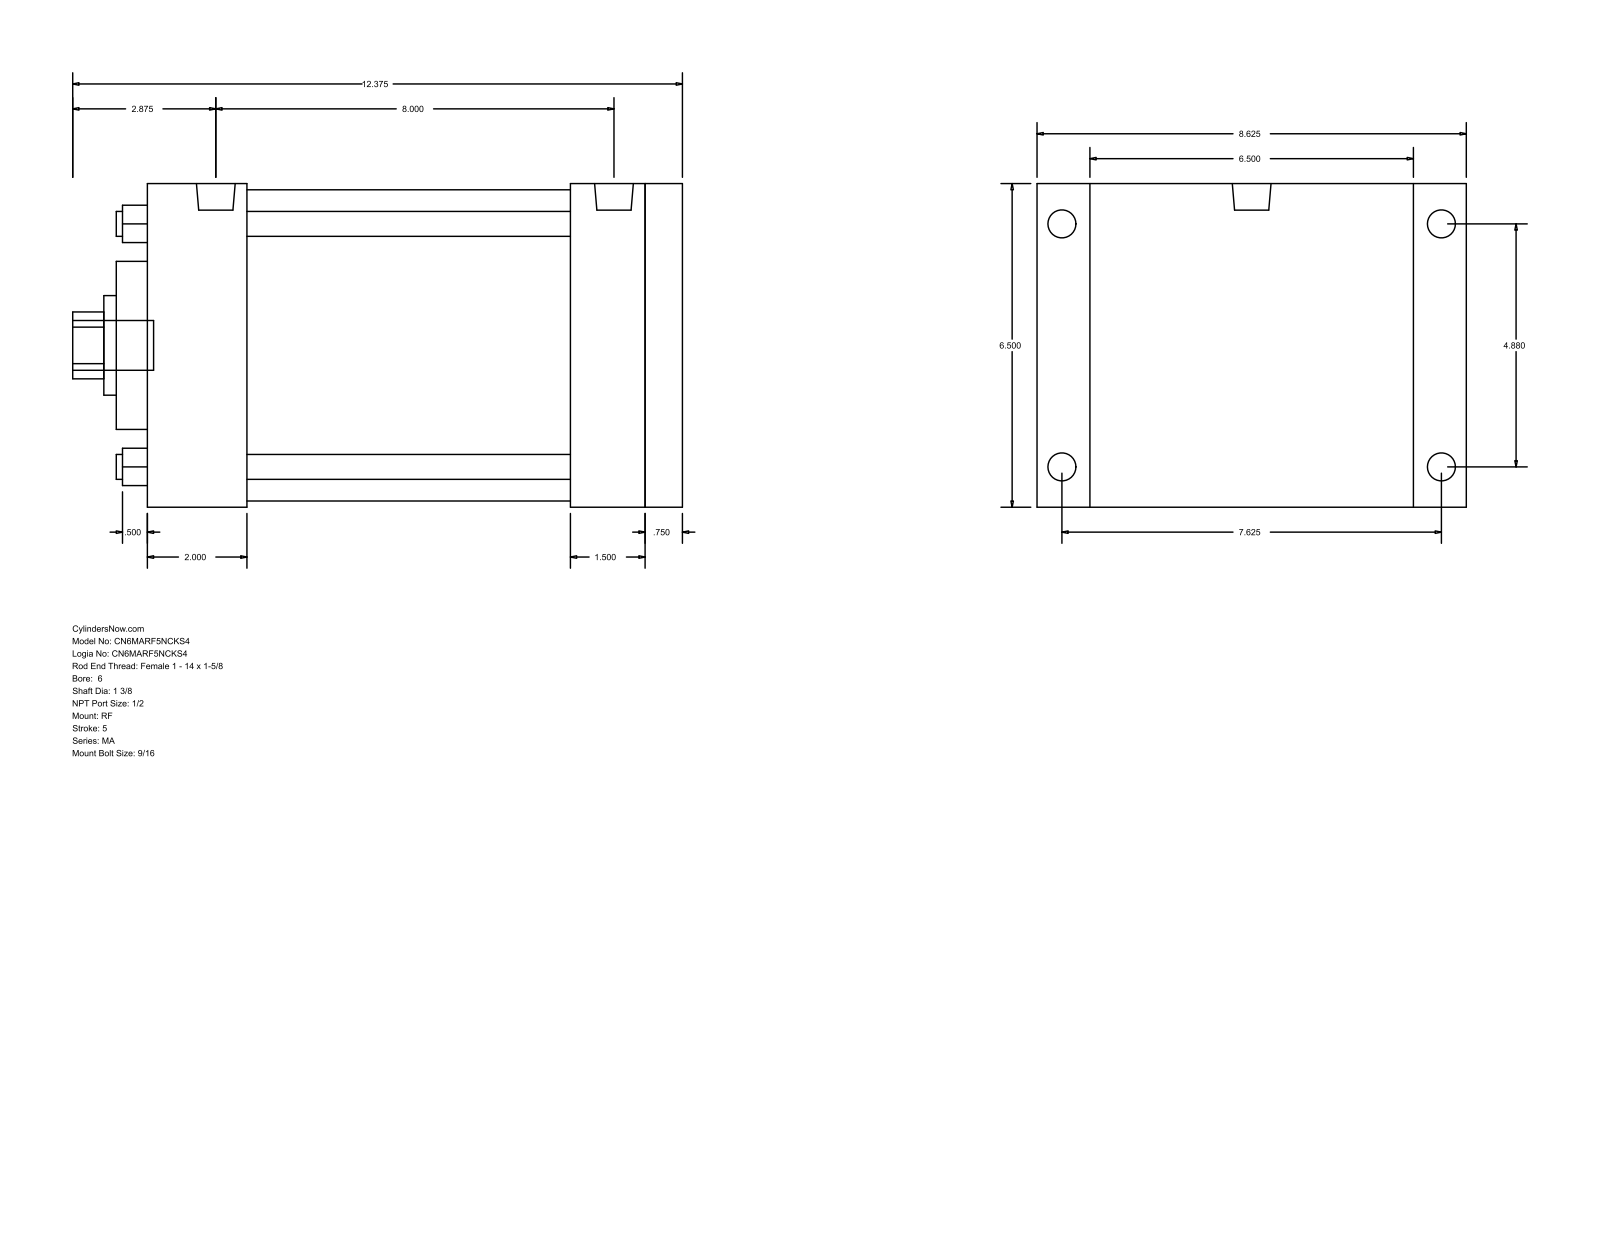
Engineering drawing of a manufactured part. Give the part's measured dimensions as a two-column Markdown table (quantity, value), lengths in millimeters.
| quantity | value |
| --- | --- |
| part name | MA_RF__0600_1.375 |
| STEP written by | GSSL Pune (CONFIG_CONTROL_DESIGN) |
| units | millimeters |
| bodies | 0 solids, 94 faces (65 planar, 29 cylindrical, 0 other) |
| overall size | 314.32 × 219.07 × 165.1 |
| round holes (diameter × count) | 12.7 × 4, 34.92 × 1, 50.8 × 1, 85.72 × 1, 158.75 × 1 |
| round bosses / shafts (diameter × count) | 17.46 × 4, 14.29 × 4, 19.77 × 2, 25.4 × 1 |
| partial cylindrical surfaces (radius × count) | 17.06 × 1 |
| main face-to-face distances | 165.1, 276.22, 219.08, 19.05, 257.17, 50.8, 206.37, 225.42, 168.28, 38.09 |
| hole center spacings | 87.65, 123.96, 175.31 |
